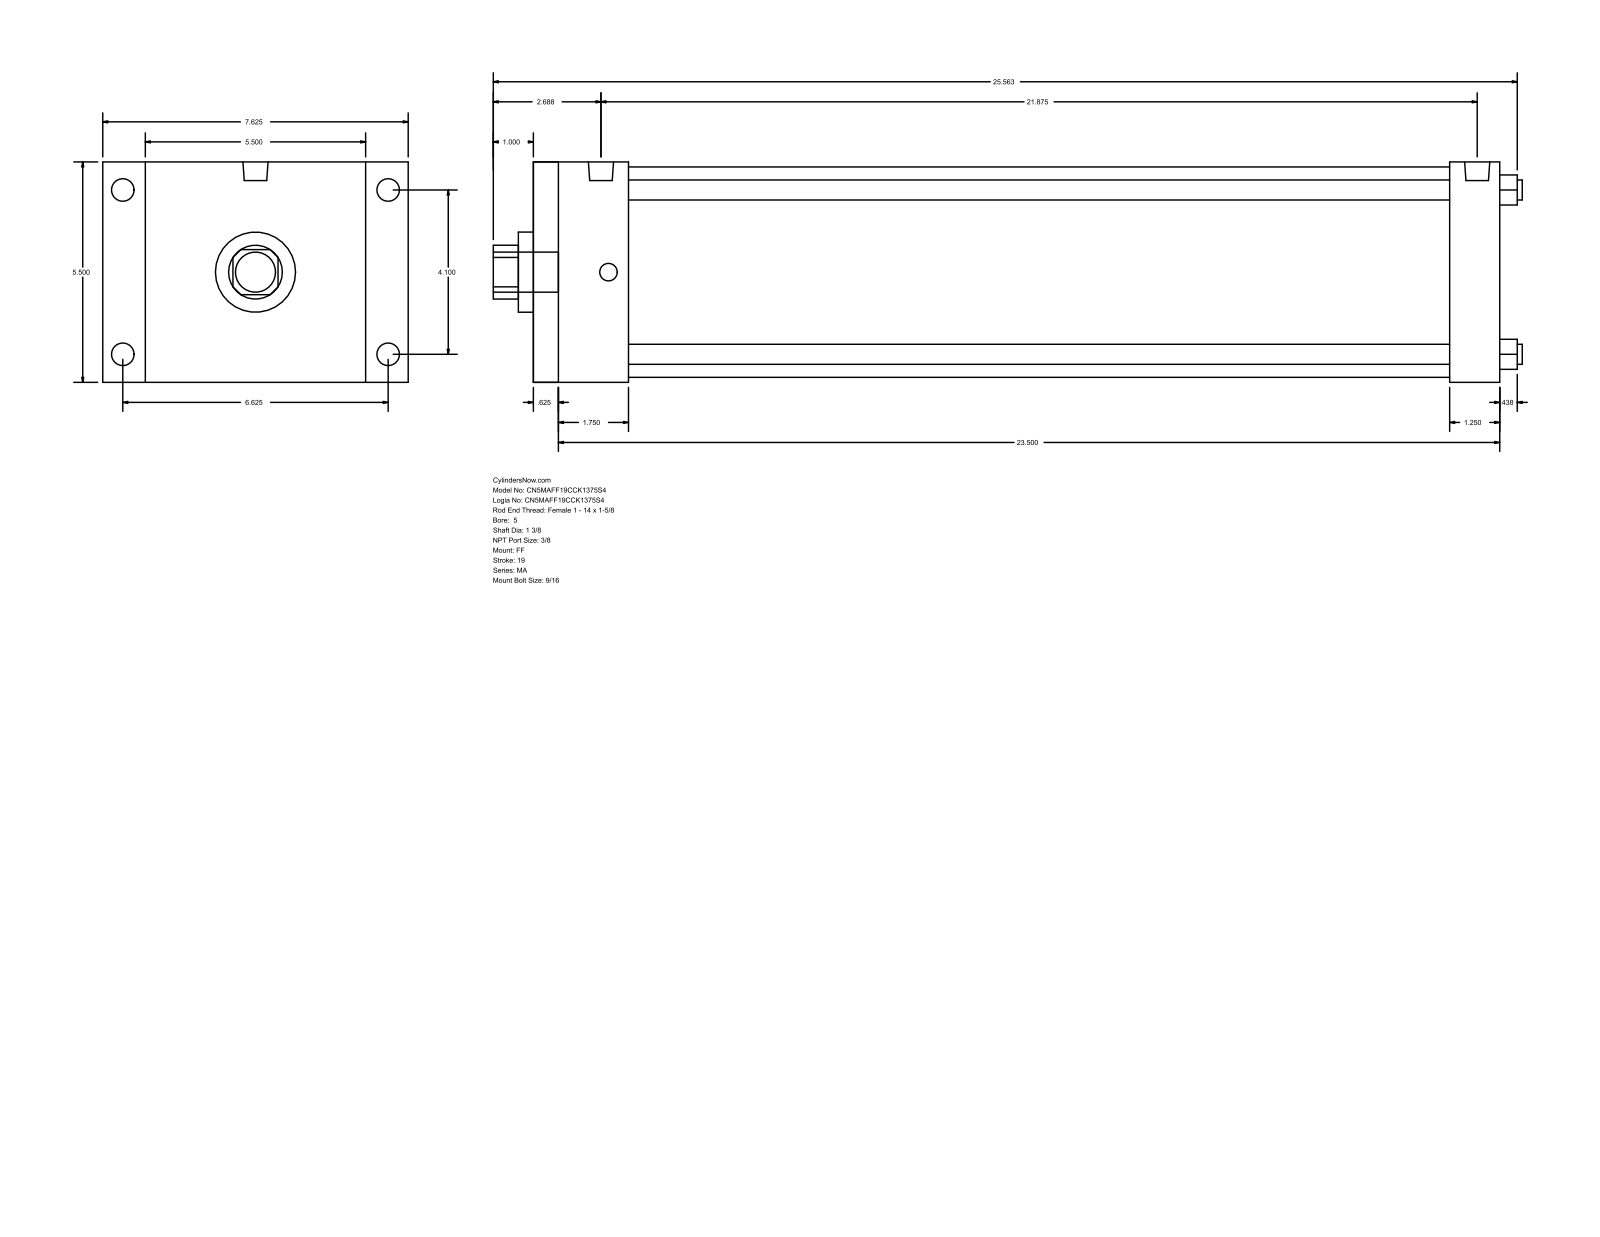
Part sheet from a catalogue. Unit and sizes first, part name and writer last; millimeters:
Units: millimetres
Overall size (bounding box): 652.46 × 193.68 × 139.7
Round holes (diameter × count): ⌀12.7 ×4, ⌀34.92 ×1, ⌀50.8 ×1, ⌀133.35 ×1
Round bosses / shafts (diameter × count): ⌀14.29 ×4, ⌀11.11 ×4, ⌀15.93 ×2, ⌀25.4 ×1
Partial cylindrical surfaces — rounded edges, fillets, slot ends (radius × count): R17.06 ×1
Main face-to-face distances: 139.7, 612.77, 15.87, 596.9, 581.02, 565.15, 31.75, 60.32, 44.45, 520.7
Hole centre spacings: 73.64, 104.14, 147.28
Bodies: 0 solids, 92 faces (64 planar, 28 cylindrical, 0 other)
Part name (STEP PRODUCT): MA_FF__0500_1.375
STEP written by: GSSL Pune (CONFIG_CONTROL_DESIGN)
